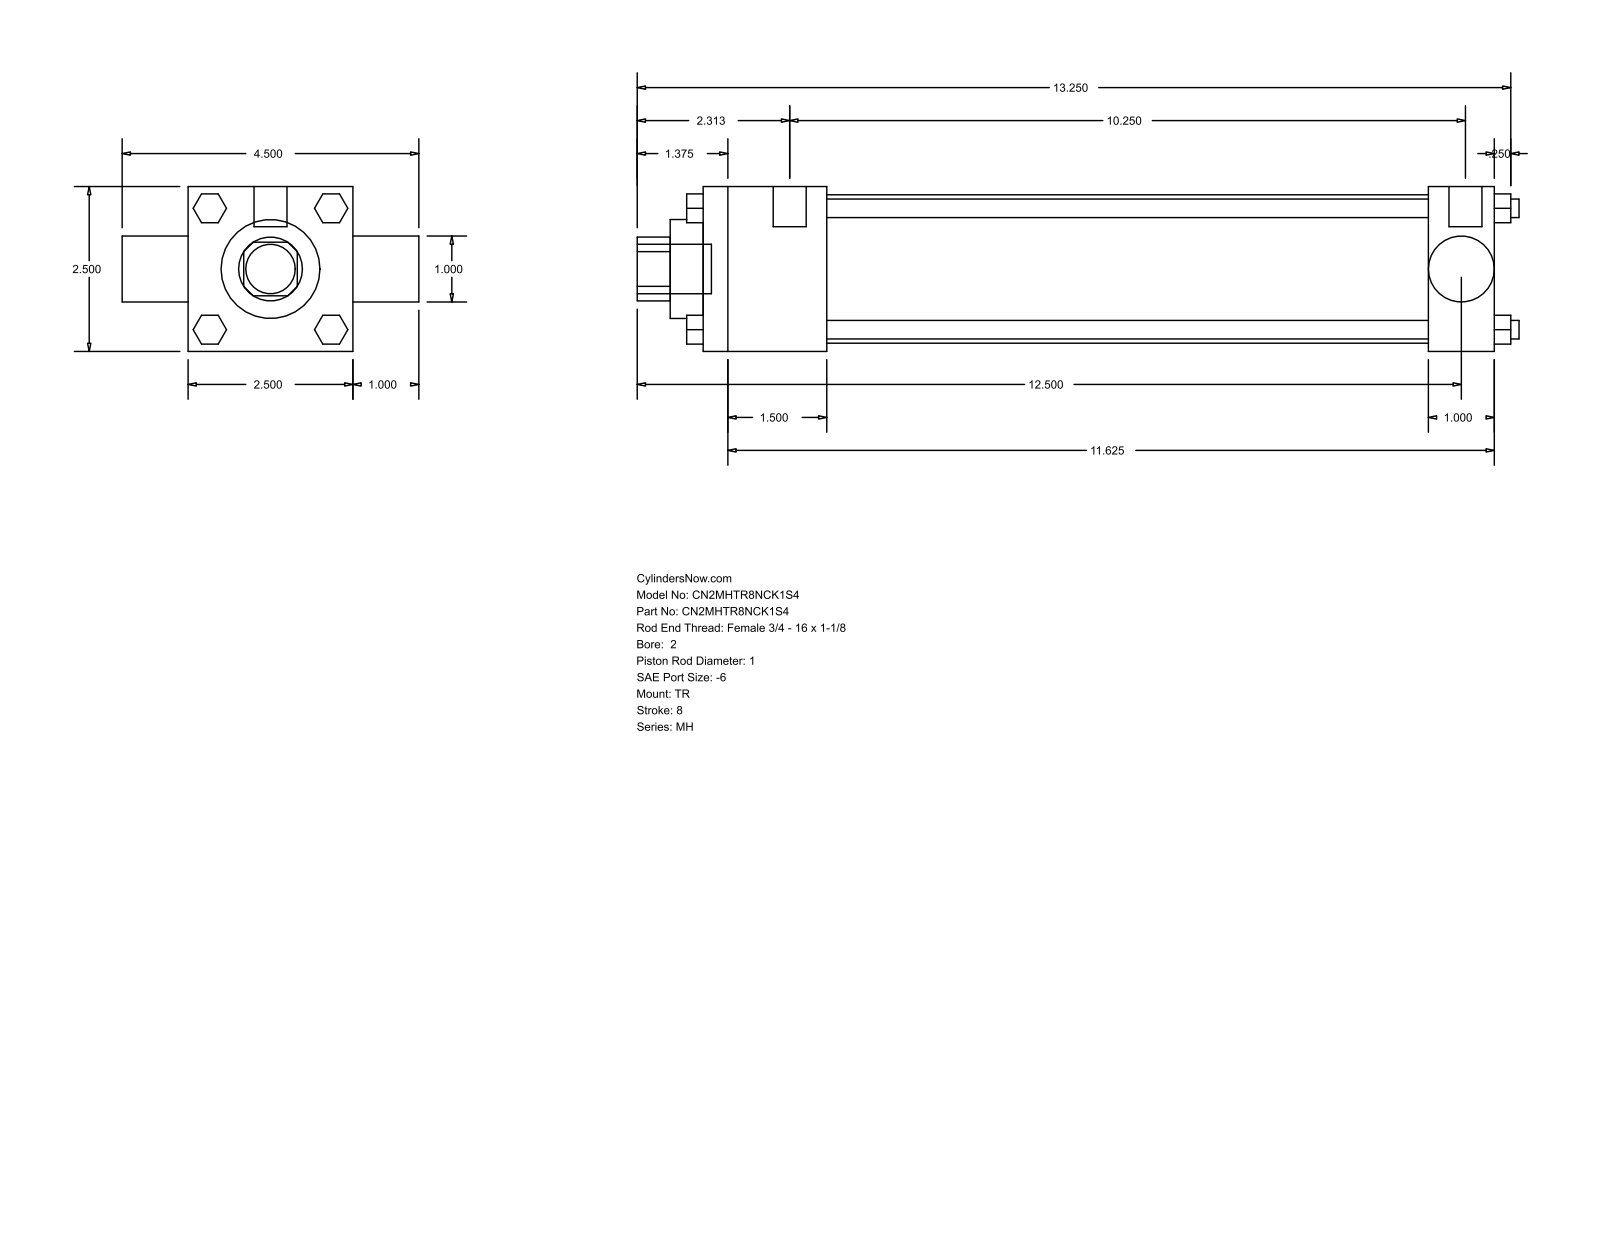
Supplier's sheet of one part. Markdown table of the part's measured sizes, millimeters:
| quantity | value |
| --- | --- |
| part name | MH_TR__0200_1 |
| STEP written by | GSSL Pune (CONFIG_CONTROL_DESIGN) |
| units | millimeters |
| bodies | 0 solids, 120 faces (92 planar, 28 cylindrical, 0 other) |
| overall size | 339.73 × 114.3 × 63.5 |
| round holes (diameter × count) | 25.35 × 1, 25.4 × 1, 38.1 × 1, 57.15 × 1 |
| round bosses / shafts (diameter × count) | 7.14 × 4, 5.56 × 3, 12.7 × 2, 19.05 × 1 |
| partial cylindrical surfaces (radius × count) | 12.29 × 1 |
| main face-to-face distances | 63.5, 304.8, 25.4, 47.63, 279.4, 231.77, 257.17, 88.9, 317.5, 6.35 |
